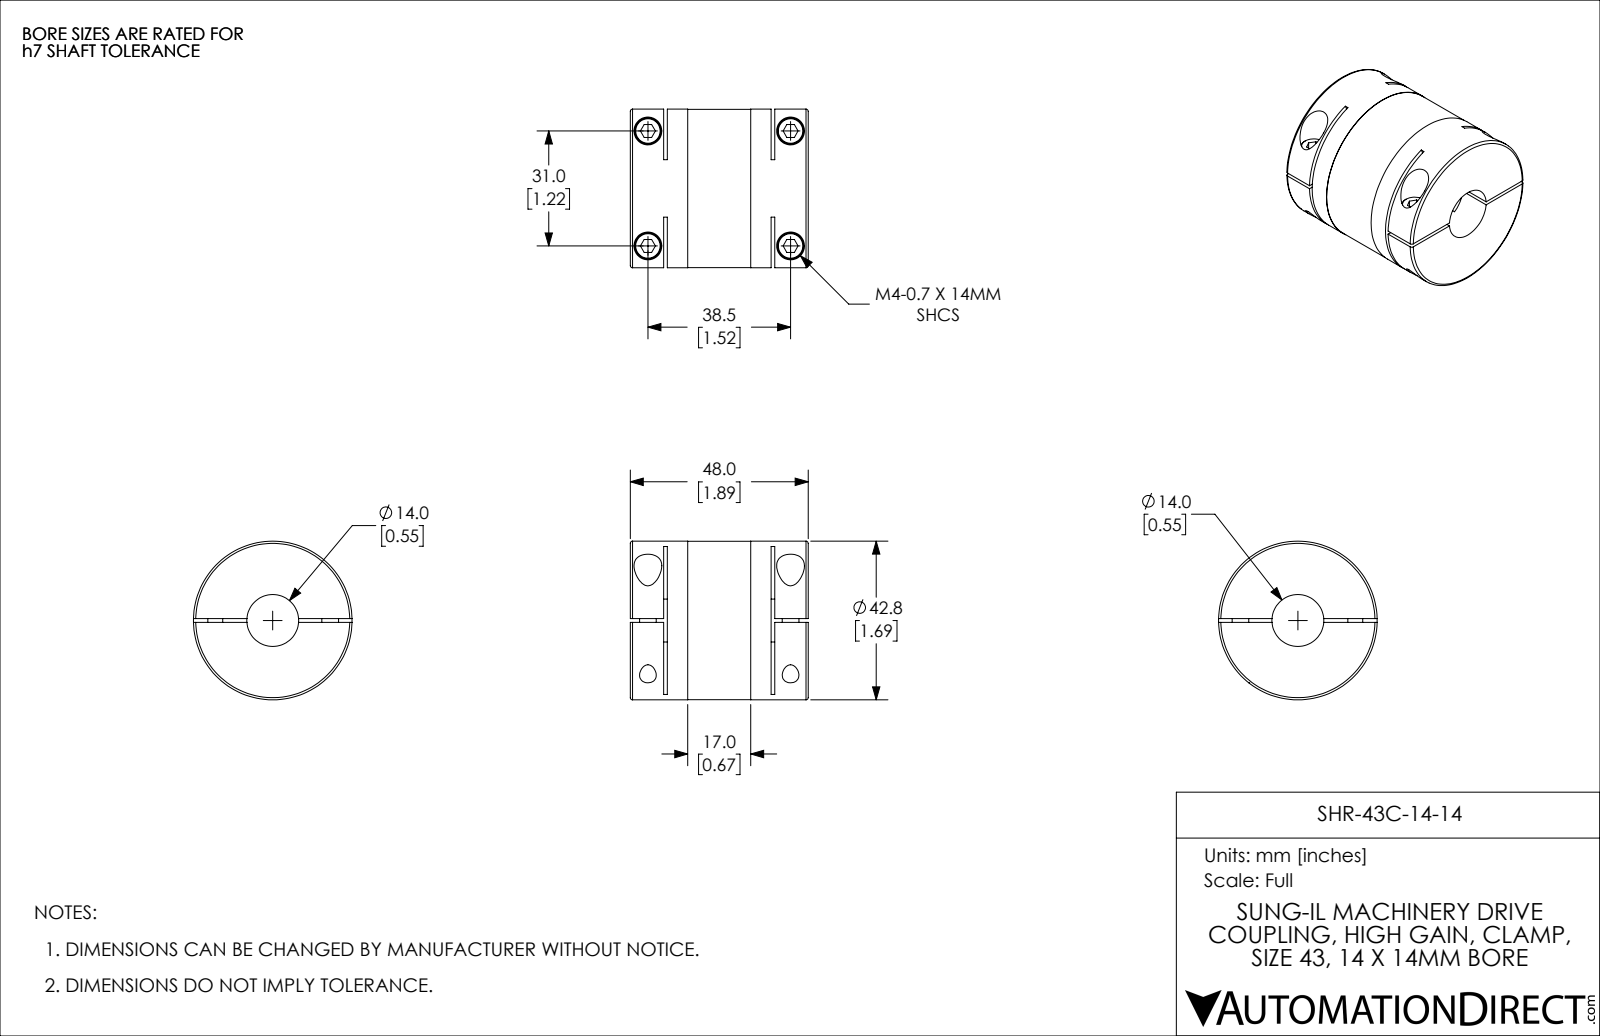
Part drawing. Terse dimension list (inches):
name: SHR-43C-14-14
written by: SolidWorks 2021 (CONFIG_CONTROL_DESIGN)
unit: in
bodies: 1 solid, 144 faces (70 planar, 58 cylindrical, 16 other)
size: 1.89 × 1.685 × 1.685
volume: 3.469 in³; area: 27.84 in²
holes: 4× ⌀0.177, 4× ⌀0.295, 1× ⌀0.551, 1× ⌀0.63
bosses: 4× ⌀0.276, 2× ⌀0.157, 1× ⌀1.685, 1× ⌀1.681
rounds: 2× R1.969
face distances: 0.039, 0.394, 1.496, 0.354, 1.535, 1.142, 1.89, 1.102, 1.181, 0.61
hole spacings: 1.22, 1.516, 1.946
